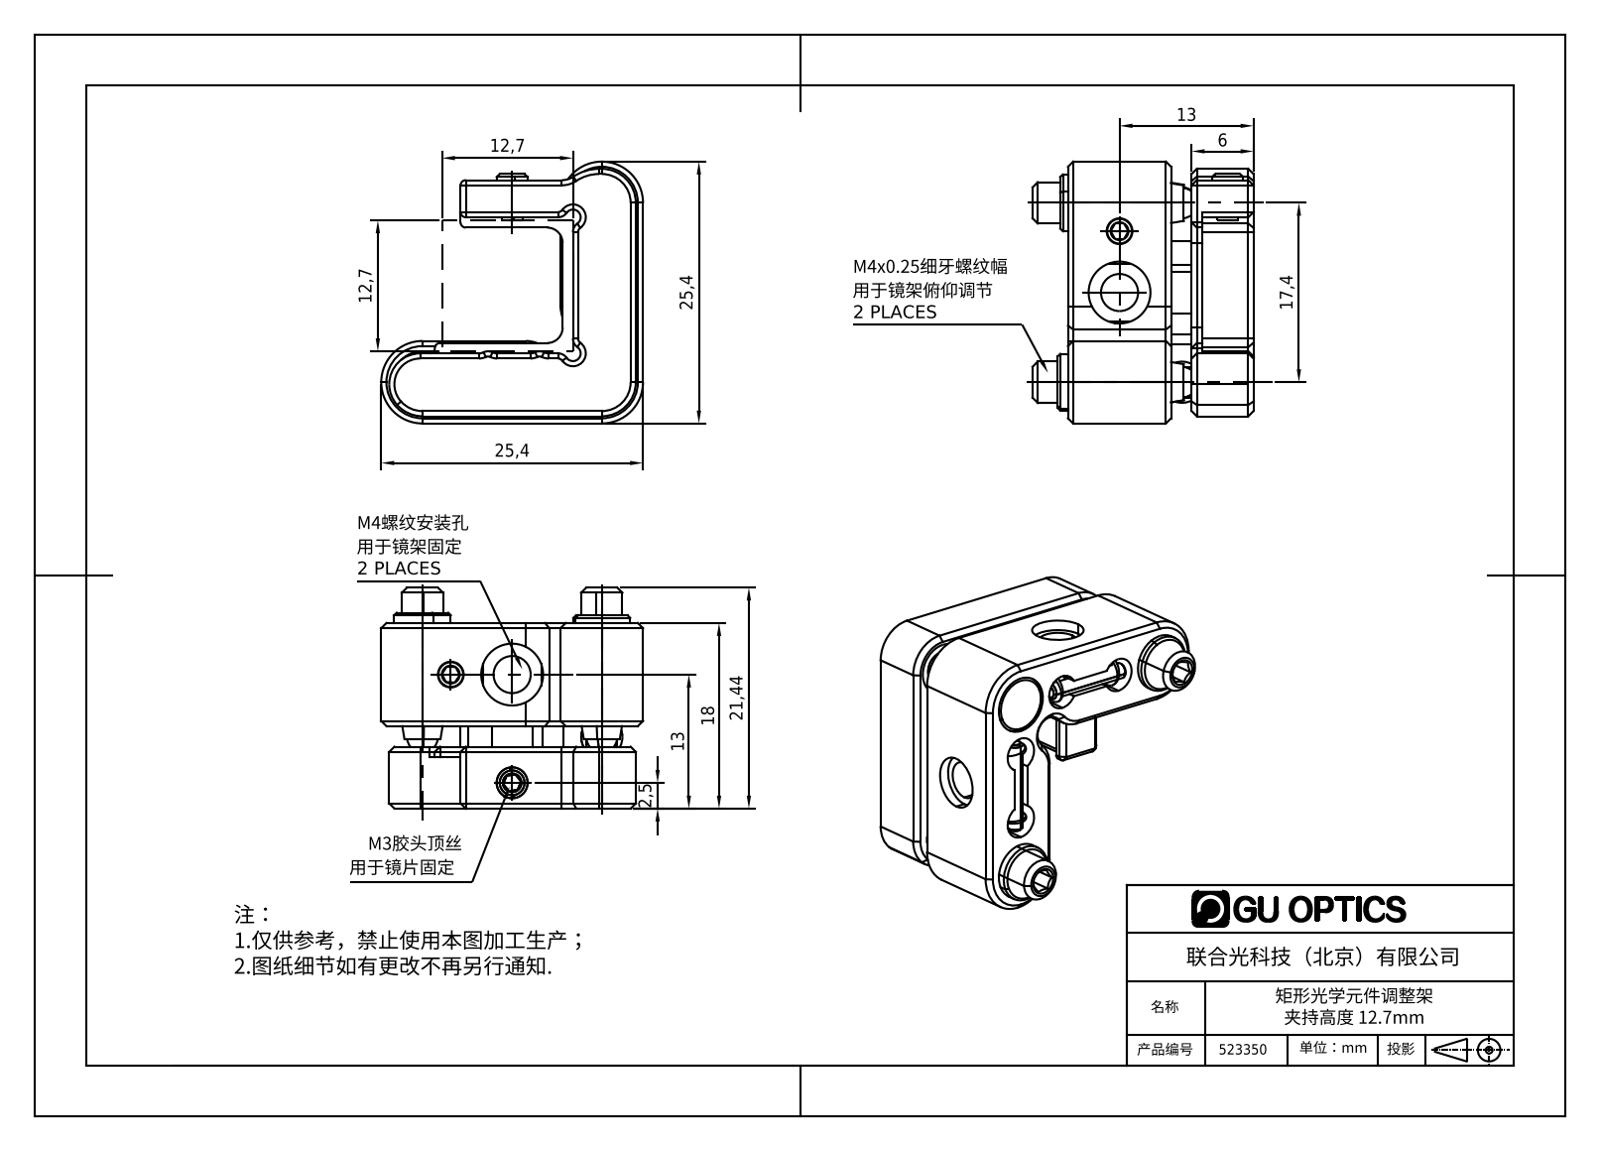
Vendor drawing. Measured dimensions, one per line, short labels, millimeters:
name: 1.1.7.4_ZJJ-R0.5-2，标准两轴矩形调整架，高度0.5英寸(12.7mm)，右手系，A
written by: SolidWorks 2018 (AUTOMOTIVE_DESIGN)
unit: mm
bodies: 0 solids, 368 faces (117 planar, 117 cylindrical, 134 other)
size: 25.4 × 25.4 × 21.43
holes: 5× ⌀6, 4× ⌀3.3, 4× ⌀3.5, 3× ⌀2.5, 3× ⌀5, 2× ⌀3.6, 1× ⌀4, 1× ⌀5.5
bosses: 5× ⌀3, 4× ⌀1.5, 2× ⌀5.8, 2× ⌀5.5, 1× ⌀4, 1× ⌀2
rounds: 10× R1, 5× R0.5, 4× R0.8, 3× R1.5, 3× R3, 3× R3.3, 3× R4, 2× R0.75
face distances: 6, 0.7, 7.99, 11.99, 1.99, 10, 17.99, 7.3, 8, 1
hole spacings: 5.2, 12.2, 5.95, 7, 13.26, 17.4, 18.16, 21.25
